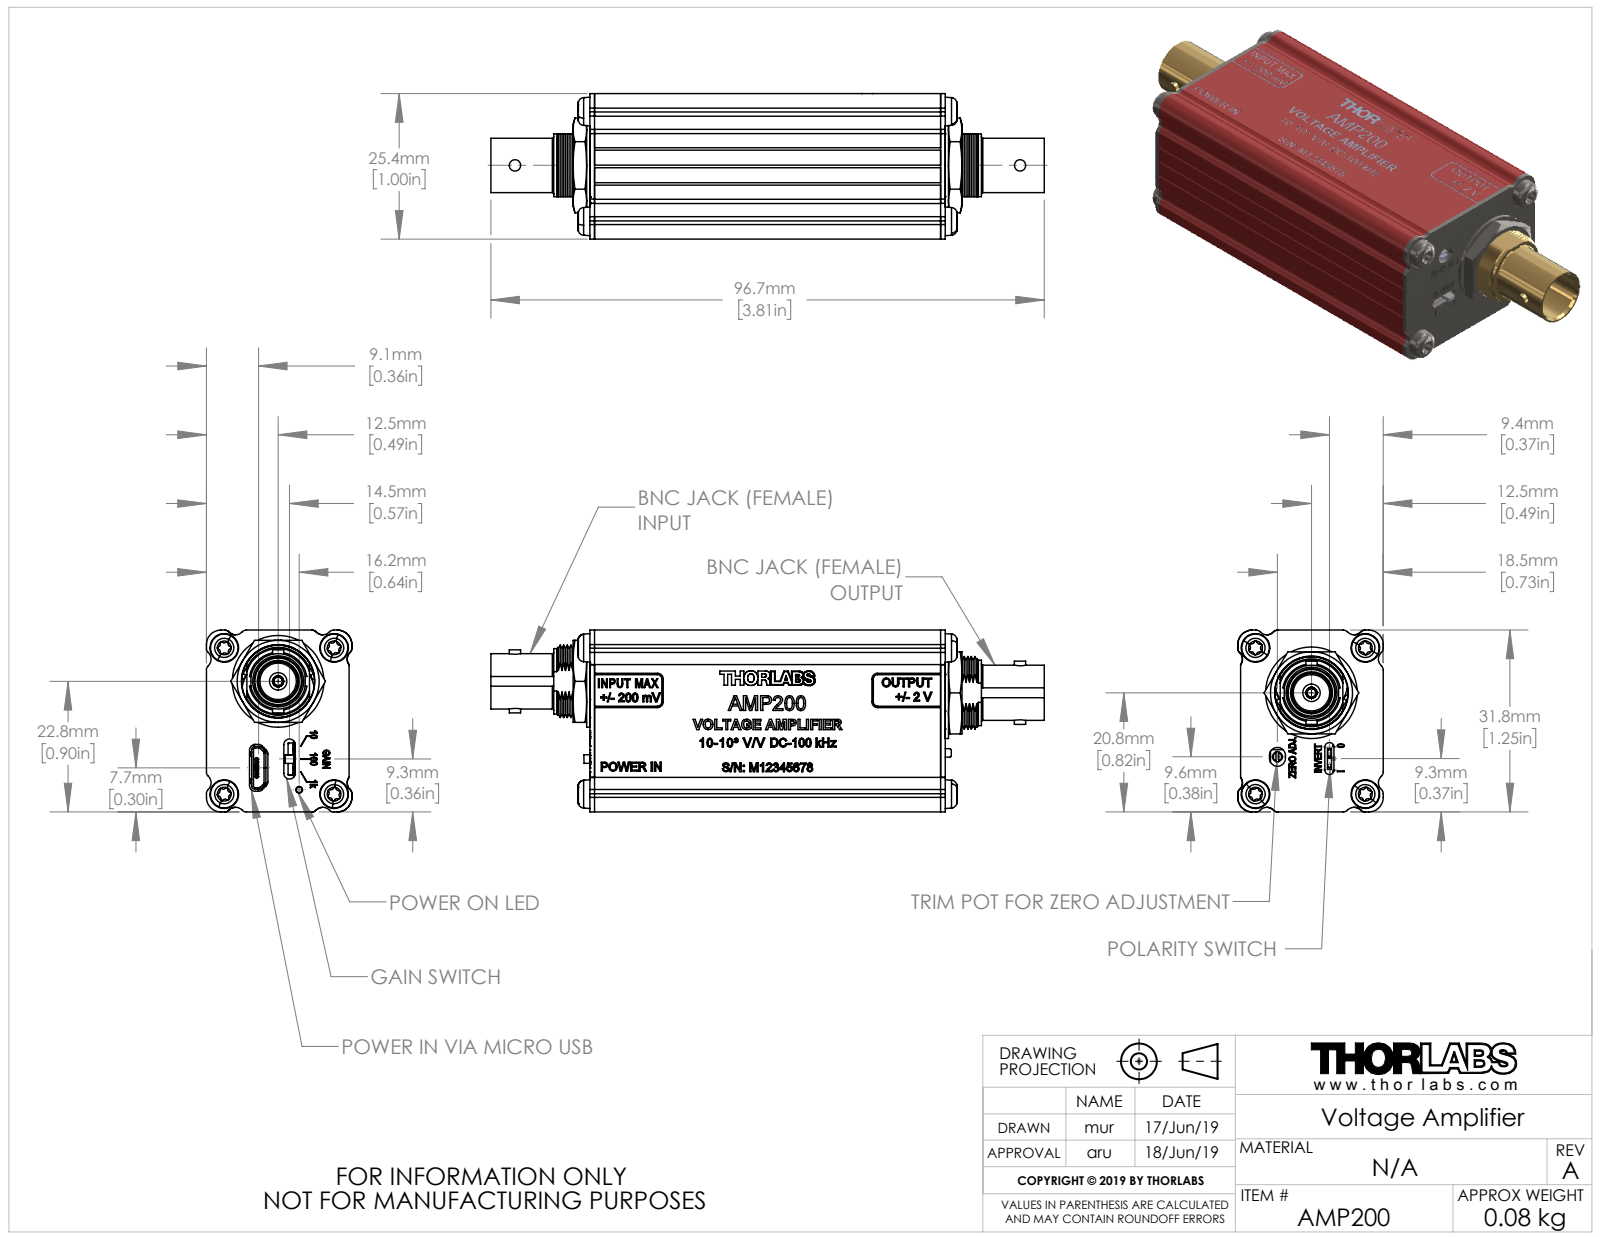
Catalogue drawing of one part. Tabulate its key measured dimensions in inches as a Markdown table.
| quantity | value |
| --- | --- |
| part name | 19.10.09_AMP200 WEB |
| STEP written by | SolidWorks 2018 (AUTOMOTIVE_DESIGN) |
| units | inches |
| bodies | 0 solids, 4796 faces (2972 planar, 798 cylindrical, 1026 other) |
| overall size | 3.805 × 1.25 × 1 |
| round holes (diameter × count) | 0.008 × 4, 0.024 × 4, 0.138 × 4, 0.033 × 2, 0.035 × 2, 0.047 × 2, 0.059 × 2, 0.076 × 2, 0.159 × 2, 0.273 × 2, 0.349 × 2, 0.5 × 2 |
| round bosses / shafts (diameter × count) | 0.018 × 6, 0.098 × 4, 0.087 × 4, 0.63 × 2, 0.45 × 2, 0.412 × 2, 0.38 × 2, 0.272 × 2 |
| partial cylindrical surfaces (radius × count) | 0.009 × 48, 0.017 × 48, 0.008 × 40, 0.004 × 37, 0.04 × 26, 0.006 × 23, 0.01 × 14, 0.063 × 14 |
| main face-to-face distances | 0.05, 0.12, 0.065, 0.472, 0.031, 0.36, 0.24, 0.48, 2.411, 0.17 |
| hole center spacings | 0.079, 0.044, 0.197, 0.118, 0.157, 0.32, 0.432, 0.507 |
